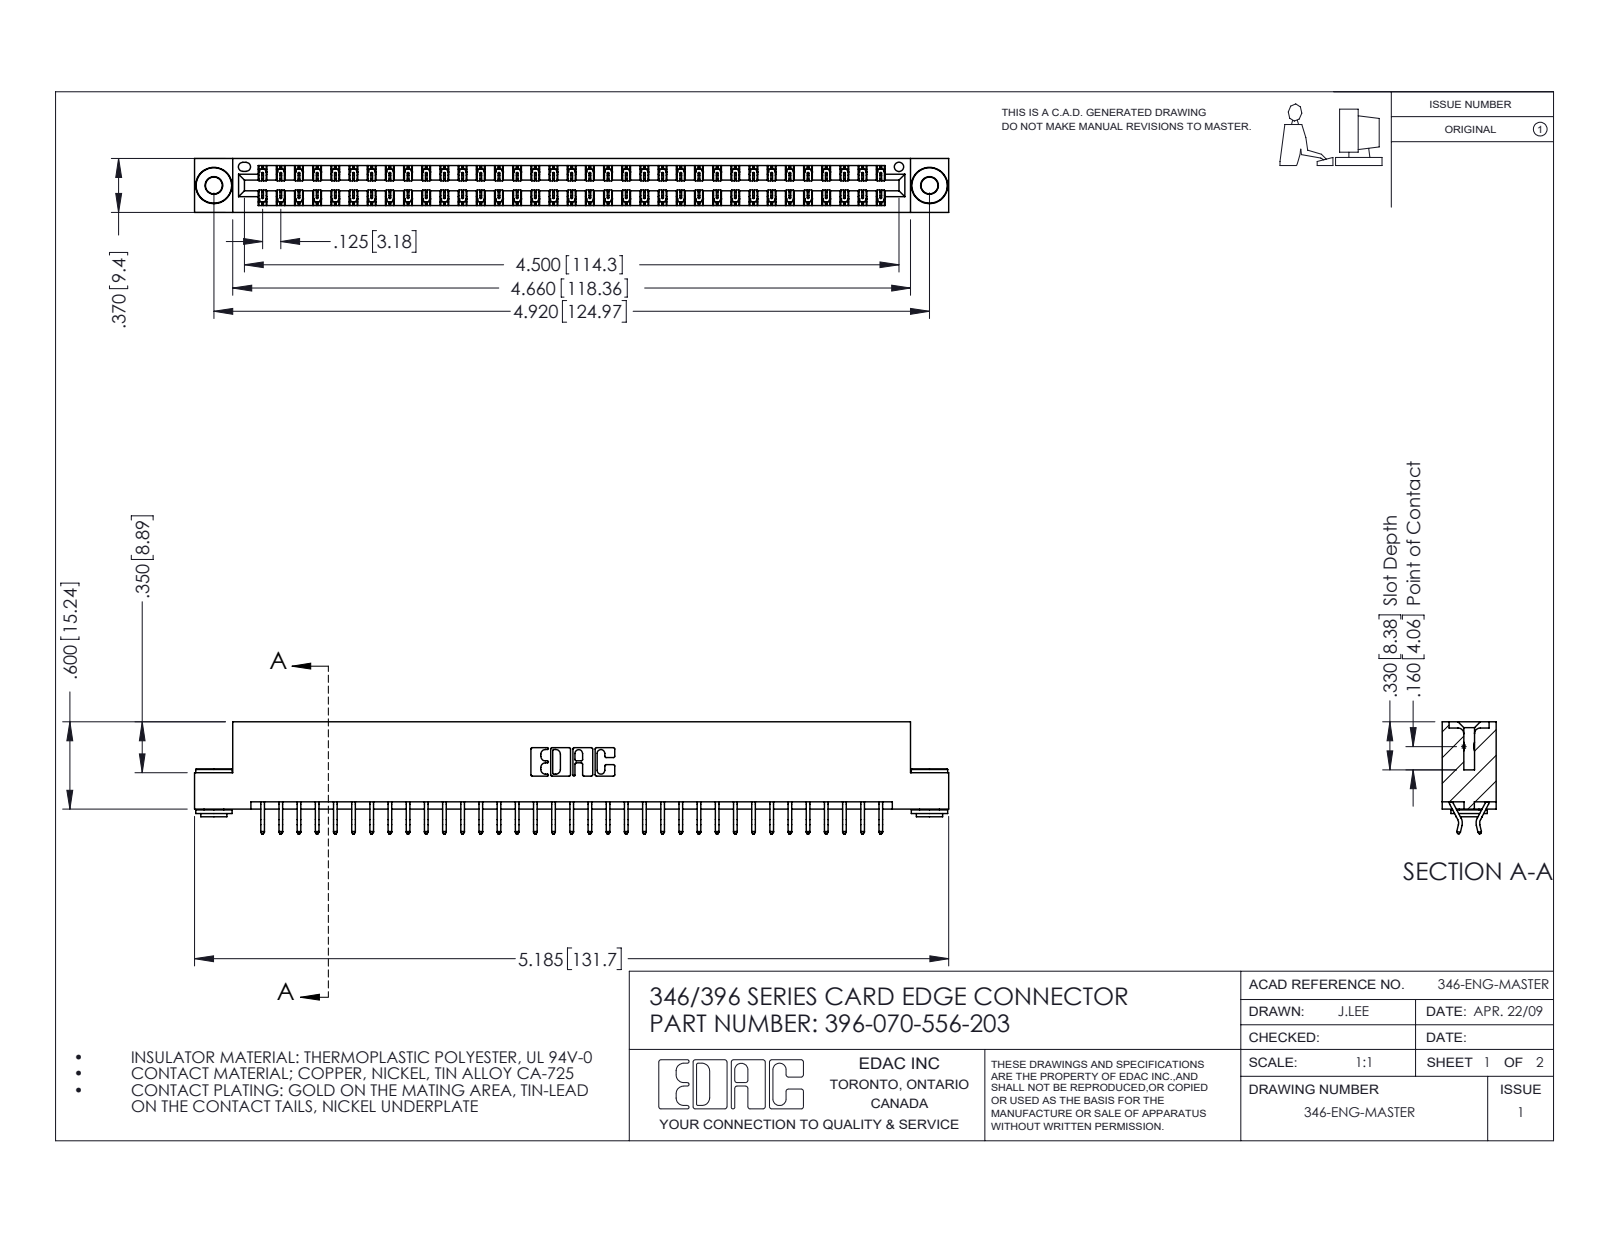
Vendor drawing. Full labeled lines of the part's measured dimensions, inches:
Part name (STEP PRODUCT): 346 Part_Flush Mounting Lugs - 0.156 Dia-TH; 396-070-556-203; 345-250-002_345-250-002-102; 345-292-001_556 Tail
STEP written by: SolidWorks 2016 (CONFIG_CONTROL_DESIGN)
Units: inches
Bodies: 73 solids, 4220 faces (2816 planar, 1396 cylindrical, 8 other)
Overall size (bounding box): 5.185 × 0.77 × 0.37
Volume: 0.781 in³ · Surface area: 27.34 in²
Round holes (diameter × count): ⌀0.116 ×2, ⌀0.156 ×2, ⌀0.064 ×1
Round bosses / shafts (diameter × count): ⌀0.25 ×2, ⌀0.18 ×2, ⌀0.136 ×2
Partial cylindrical surfaces — rounded edges, fillets, slot ends (radius × count): R0.006 ×105, R0.01 ×22, R0.007 ×6, R0.031 ×6, R0.026 ×3, R0.01 ×2, R0.014 ×2, R0.022 ×2
Main face-to-face distances: 0.048, 0.322, 0.37, 0.25, 0.025, 0.072, 0.298, 0.275, 0.148, 0.222
Hole centre spacings: 0.246, 4.711, 4.92
